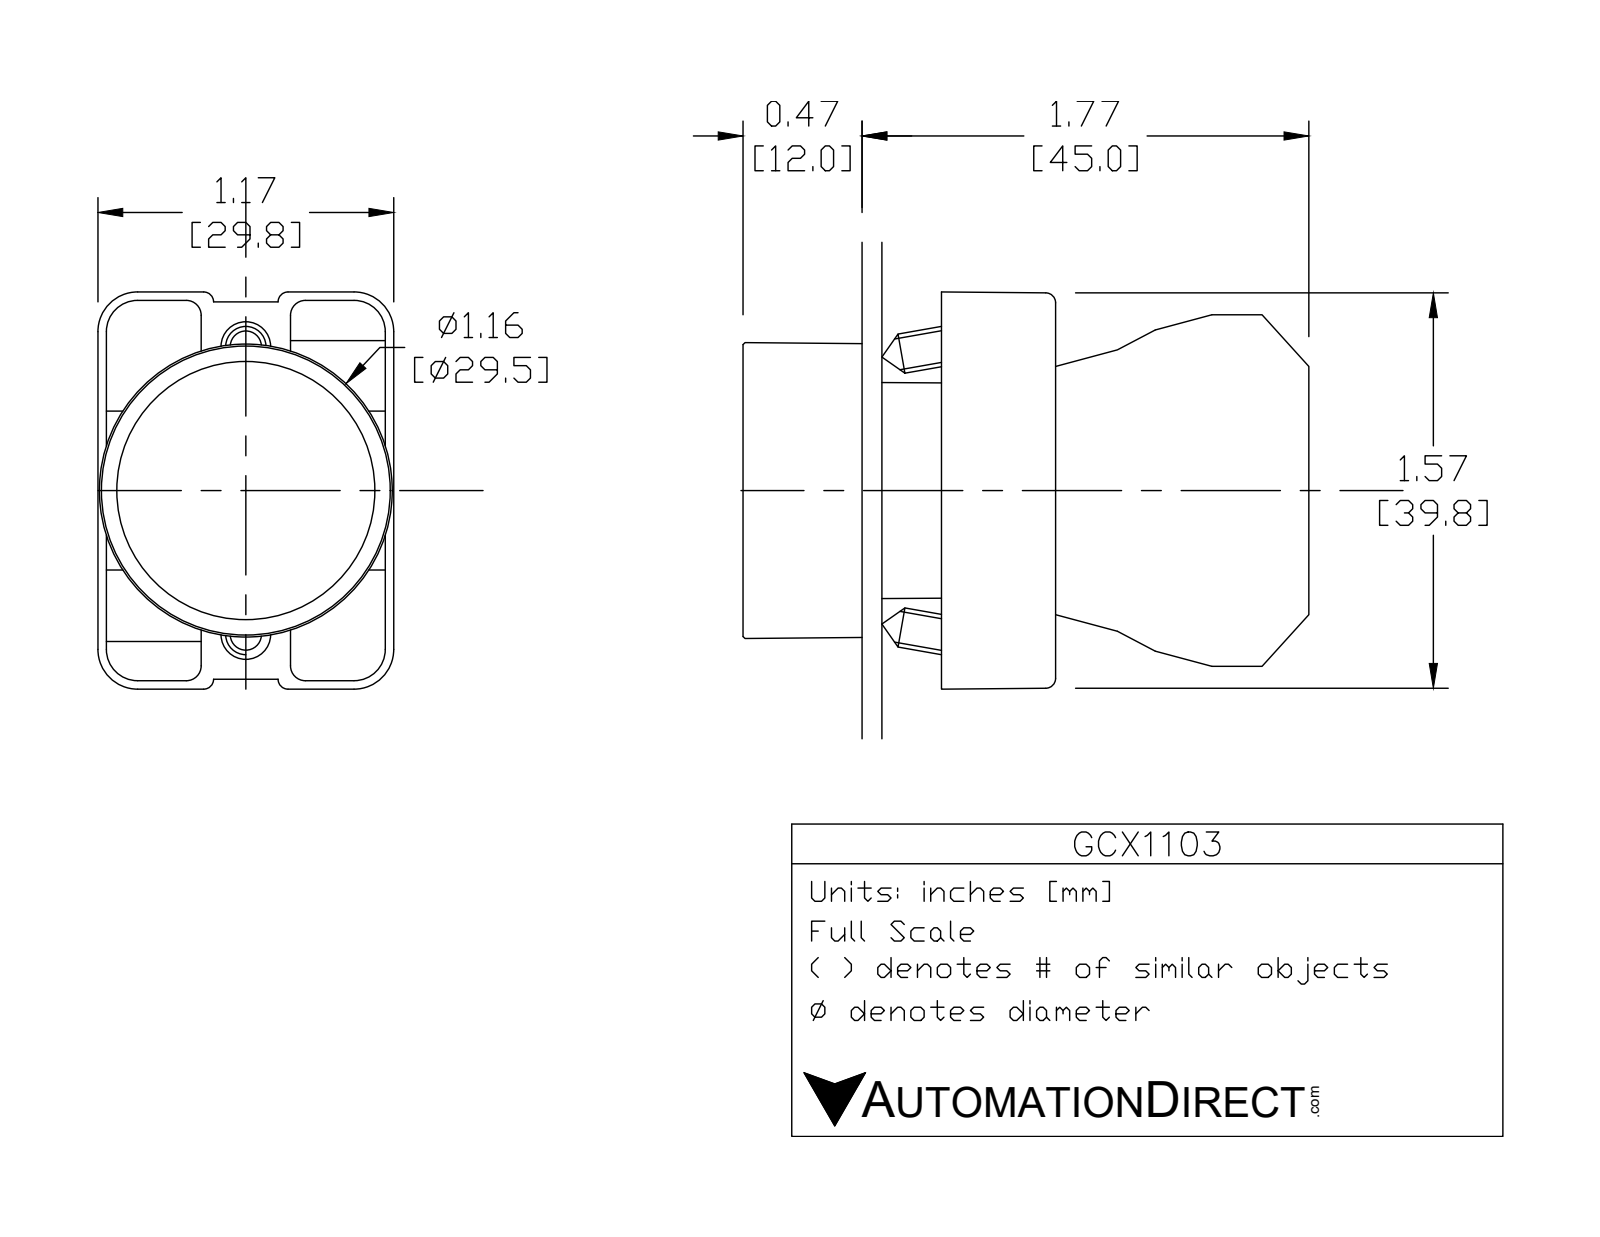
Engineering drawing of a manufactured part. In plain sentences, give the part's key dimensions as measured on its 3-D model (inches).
The part is named "GCX1103 OPERATOR; GCX1103; ecx1029; ecx1040". Its 3-D file was written by "SolidWorks 2016 (AUTOMOTIVE_DESIGN)". It is 6 solids with 381 faces: 222 planar, 132 cylindrical and 27 other. Overall it measures 2.217 by 1.581 by 1.177 inches. Its volume is 1.741 cubic inches and its surface area 27.14 square inches. Round holes: 2 of diameter 0.079, 2 of diameter 0.124, 2 of diameter 0.13, 1 of diameter 0.087, 1 of diameter 0.197, 1 of diameter 0.878, 1 of diameter 0.888, 1 of diameter 1.024. Round bosses or shafts: 2 of diameter 0.157, 1 of diameter 1.175, 1 of diameter 1.004, 1 of diameter 0.945, 1 of diameter 0.856, 1 of diameter 0.78. Partial cylindrical surfaces (rounded edges, fillets, slot ends): 24 of radius 0.059, 12 of radius 0.041, 12 of radius 0.124, 12 of radius 0.157, 4 of radius 0.039, 2 of radius 0.128, 1 of radius 0.02, 1 of radius 0.063. The main face-to-face distances are 0.72, 0.579, 0.033, 0.472, 1.193, 0.031, 0.689, 0.598, 1.161, 1.071. The hole center spacings are 0.236, 0.544, 0.472, 0.49.
